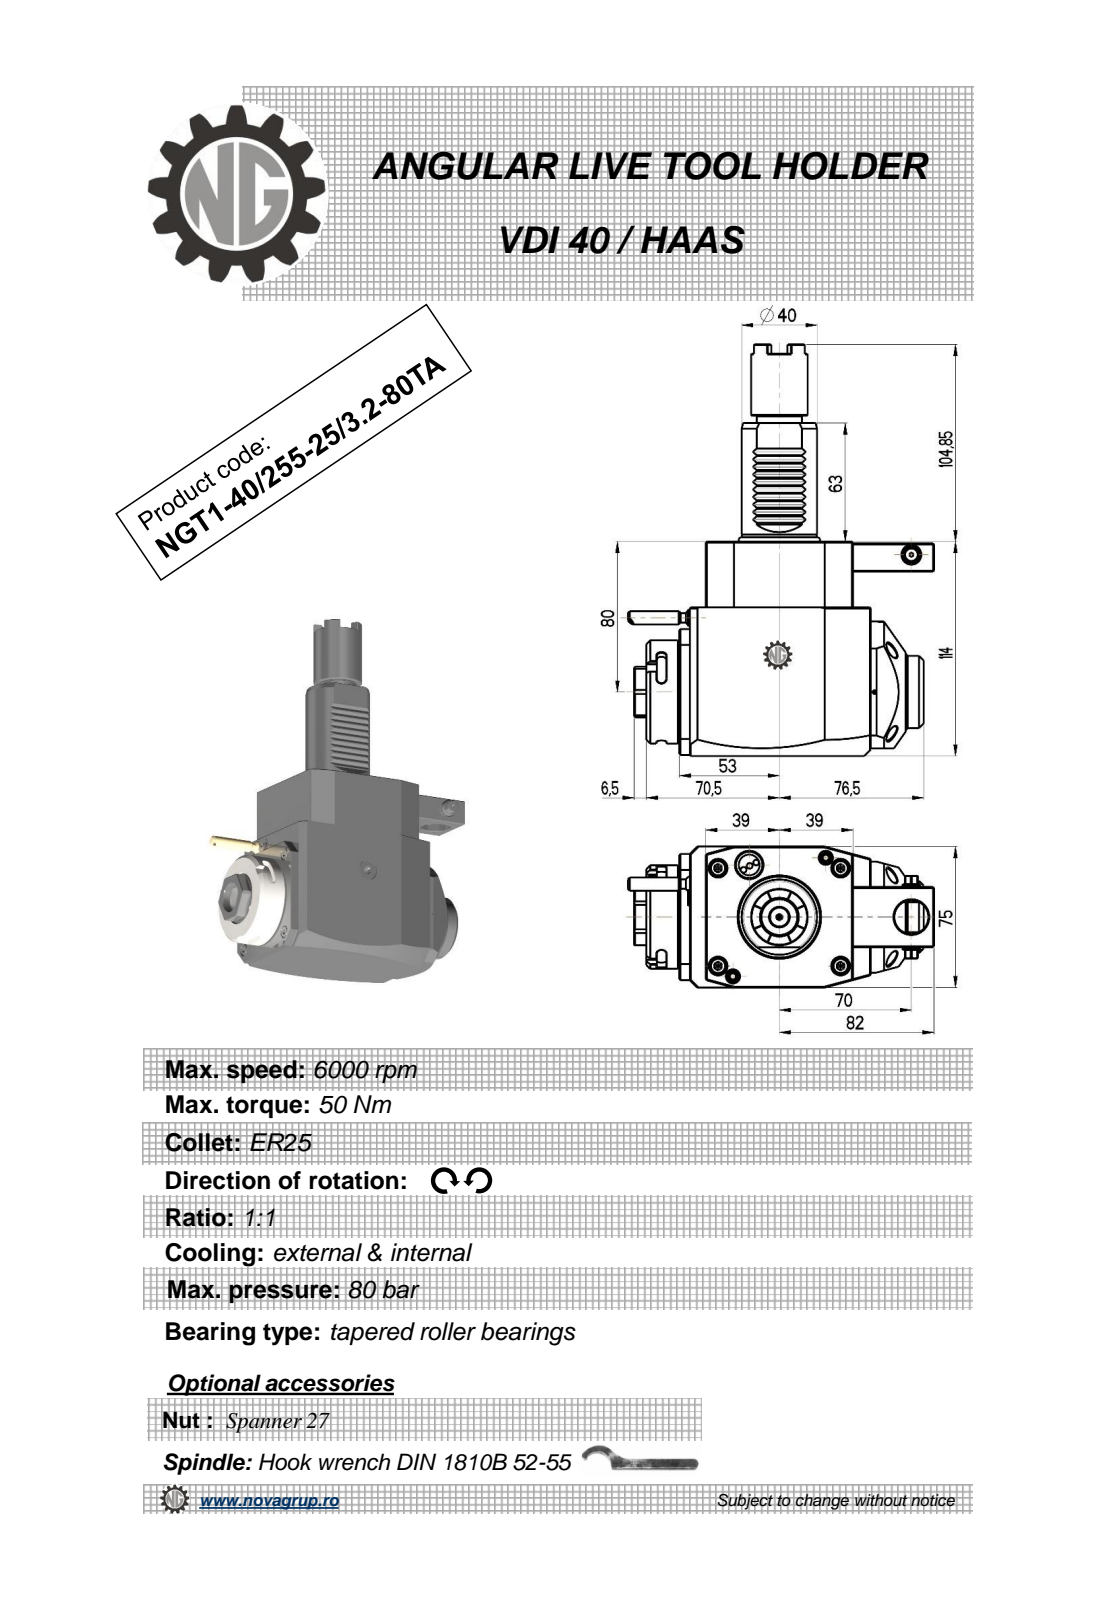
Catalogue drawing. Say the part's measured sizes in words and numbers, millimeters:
The part is named "NGT1_40_255_25_3_2_80TA". Its 3-D file was written by "PRO/ENGINEER BY PARAMETRIC TECHNOLOGY CORPORATION, 2010280 (CONFIG_CONTROL_DESIGN)". It is 1 solid with 395 faces: 213 planar, 94 cylindrical and 88 other. Overall it measures 218.85 by 162.33 by 75 millimeters. Its volume is 999 830 cubic millimeters and its surface area 77 716 square millimeters. Round holes: 2 of diameter 18, 1 of diameter 2, 1 of diameter 2.5, 1 of diameter 3, 1 of diameter 9.5. Round bosses or shafts: 2 of diameter 8.96, 1 of diameter 55, 1 of diameter 48, 1 of diameter 40, 1 of diameter 38.5, 1 of diameter 30, 1 of diameter 20, 1 of diameter 10. Partial cylindrical surfaces (rounded edges, fillets, slot ends): 10 of radius 0.3, 6 of radius 2.5, 2 of radius 180, 1 of radius 0.5, 1 of radius 3.85, 1 of radius 4.25, 1 of radius 15, 1 of radius 24.5. The main face-to-face distances are 75, 114, 14, 17.5, 79, 109.5, 92, 78, 98, 31.5. The hole center spacings are 37.35, 43.2, 72.5.
